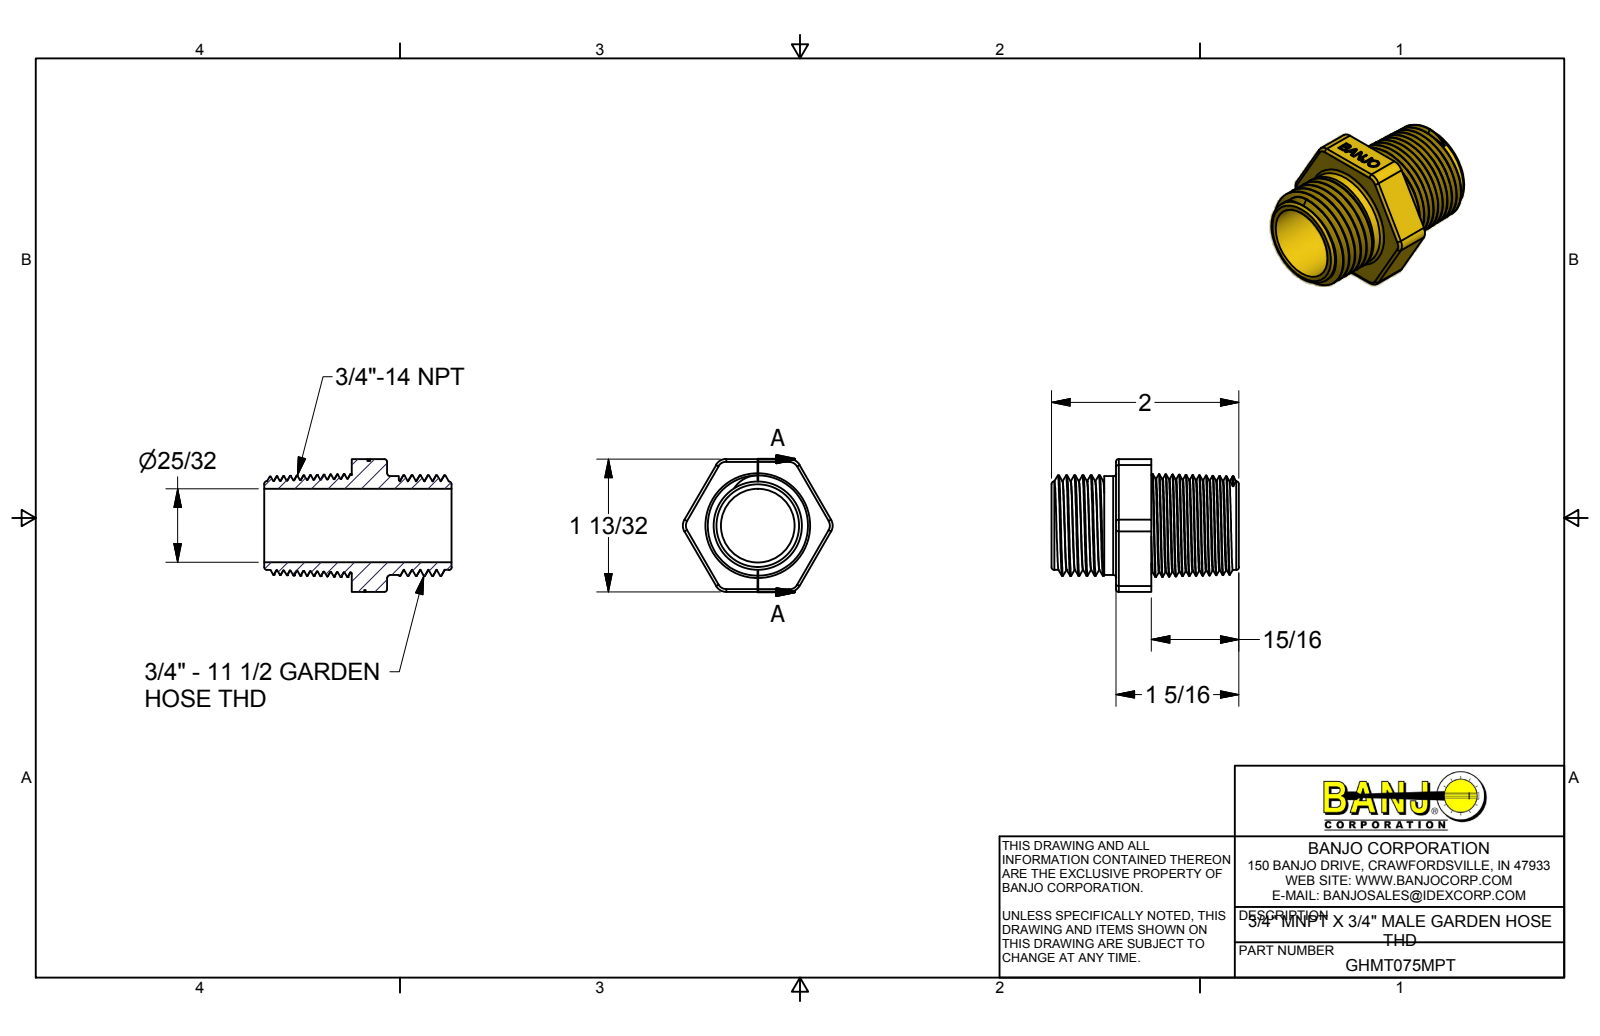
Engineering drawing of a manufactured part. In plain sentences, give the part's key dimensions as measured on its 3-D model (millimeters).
The part is named "GHMT075MPTZ; GHMT075MPT". Its 3-D file was written by "Autodesk Inventor 2015 (AUTOMOTIVE_DESIGN)". It is 1 solid with 237 faces: 119 planar, 18 cylindrical and 100 other. Overall it measures 50.55 by 40.4 by 35.84 millimeters. Its volume is 16 291 cubic millimeters and its surface area 11 327 square millimeters. Round holes: 1 of diameter 19.81. Round bosses or shafts: 1 of diameter 27.12, 1 of diameter 26.67, 1 of diameter 23.88. Partial cylindrical surfaces (rounded edges, fillets, slot ends): 6 of radius 0.76, 6 of radius 3.17, 1 of radius 7.27, 1 of radius 7.59. The main face-to-face distances are 35.84, 9.52, 23.62, 33.14, 50.54, 26.92, 17.4, 36.32, 12.7, 3.18.
